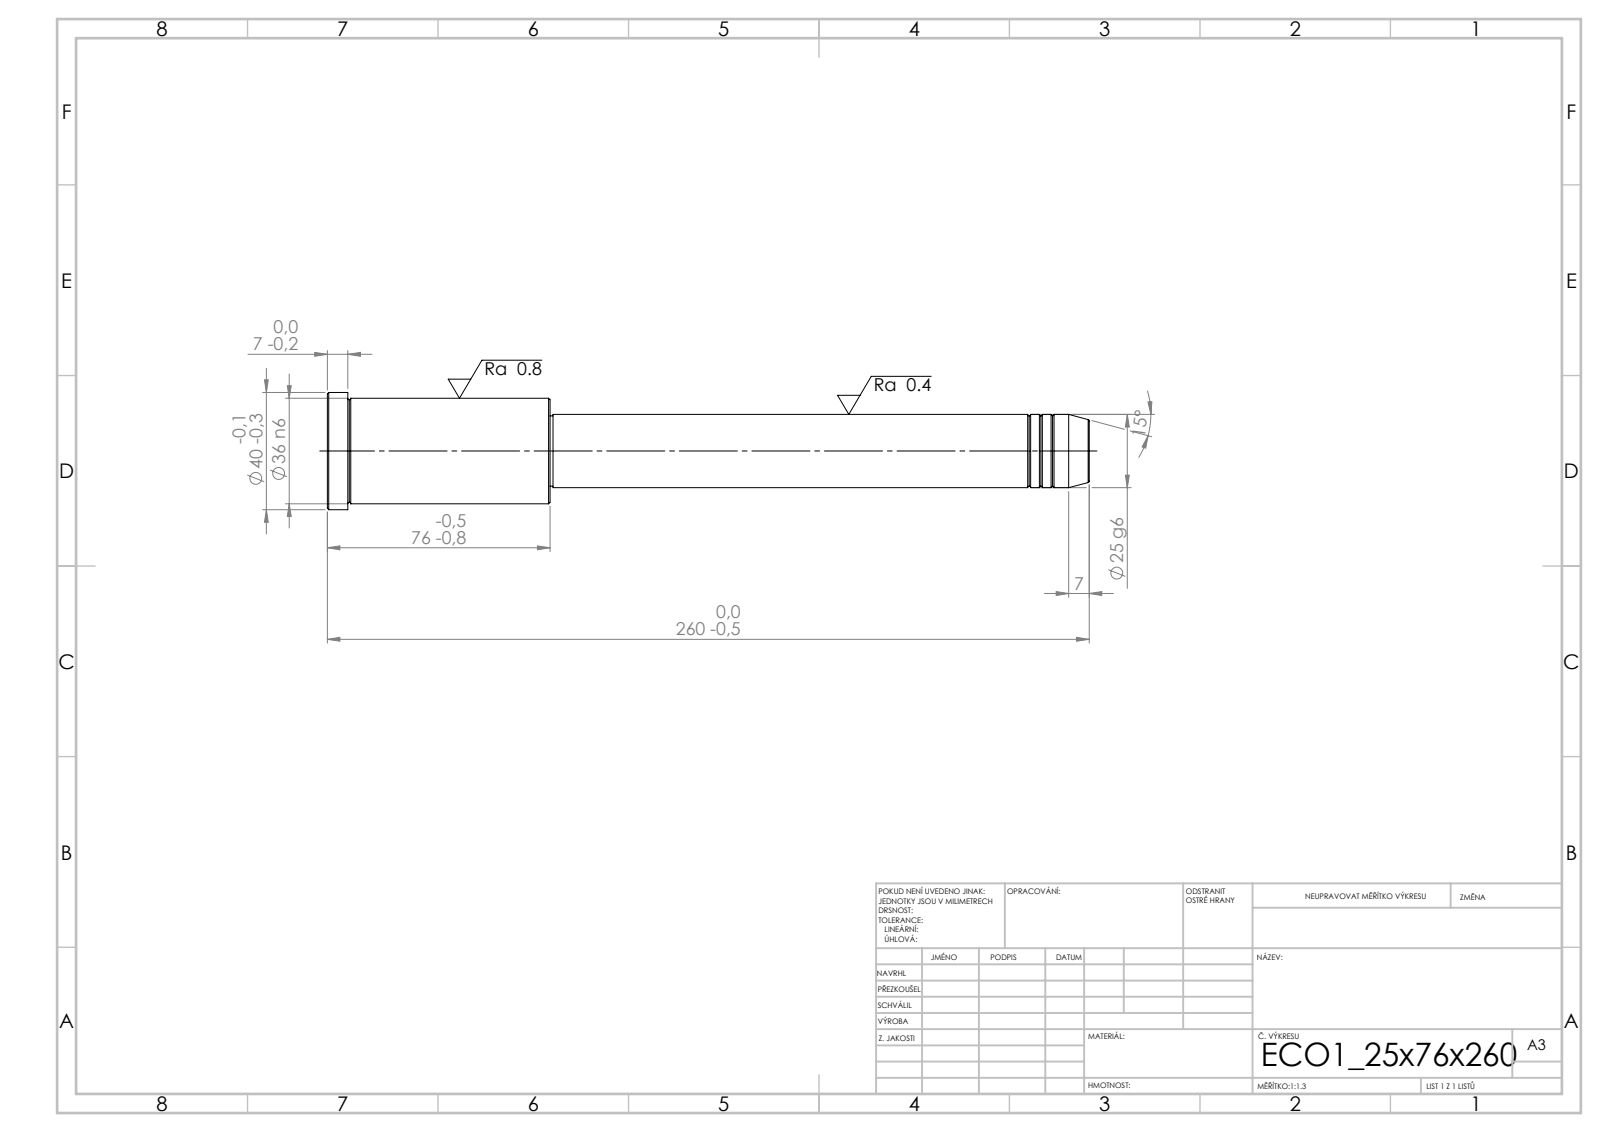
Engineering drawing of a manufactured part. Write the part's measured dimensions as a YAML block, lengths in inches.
step_written_by: "SolidWorks 2019 (CONFIG_CONTROL_DESIGN)"
units: inches
bodies: {solids: 1, faces: 43, planar: 5, cylindrical: 14, other: 24}
overall_size: [10.236, 1.575, 1.575]
volume: 10.29
surface_area: 39.79
round_bosses_or_shafts:
  - {diameter: 1.575, count: 1}
  - {diameter: 1.417, count: 1}
  - {diameter: 0.984, count: 1}
  - {diameter: 0.945, count: 1}
face_to_face_distances: [2.992, 7.244, 10.236, 9.961, 2.717, 0.276, 7.205, 0.039, 2.756, 3.031]
